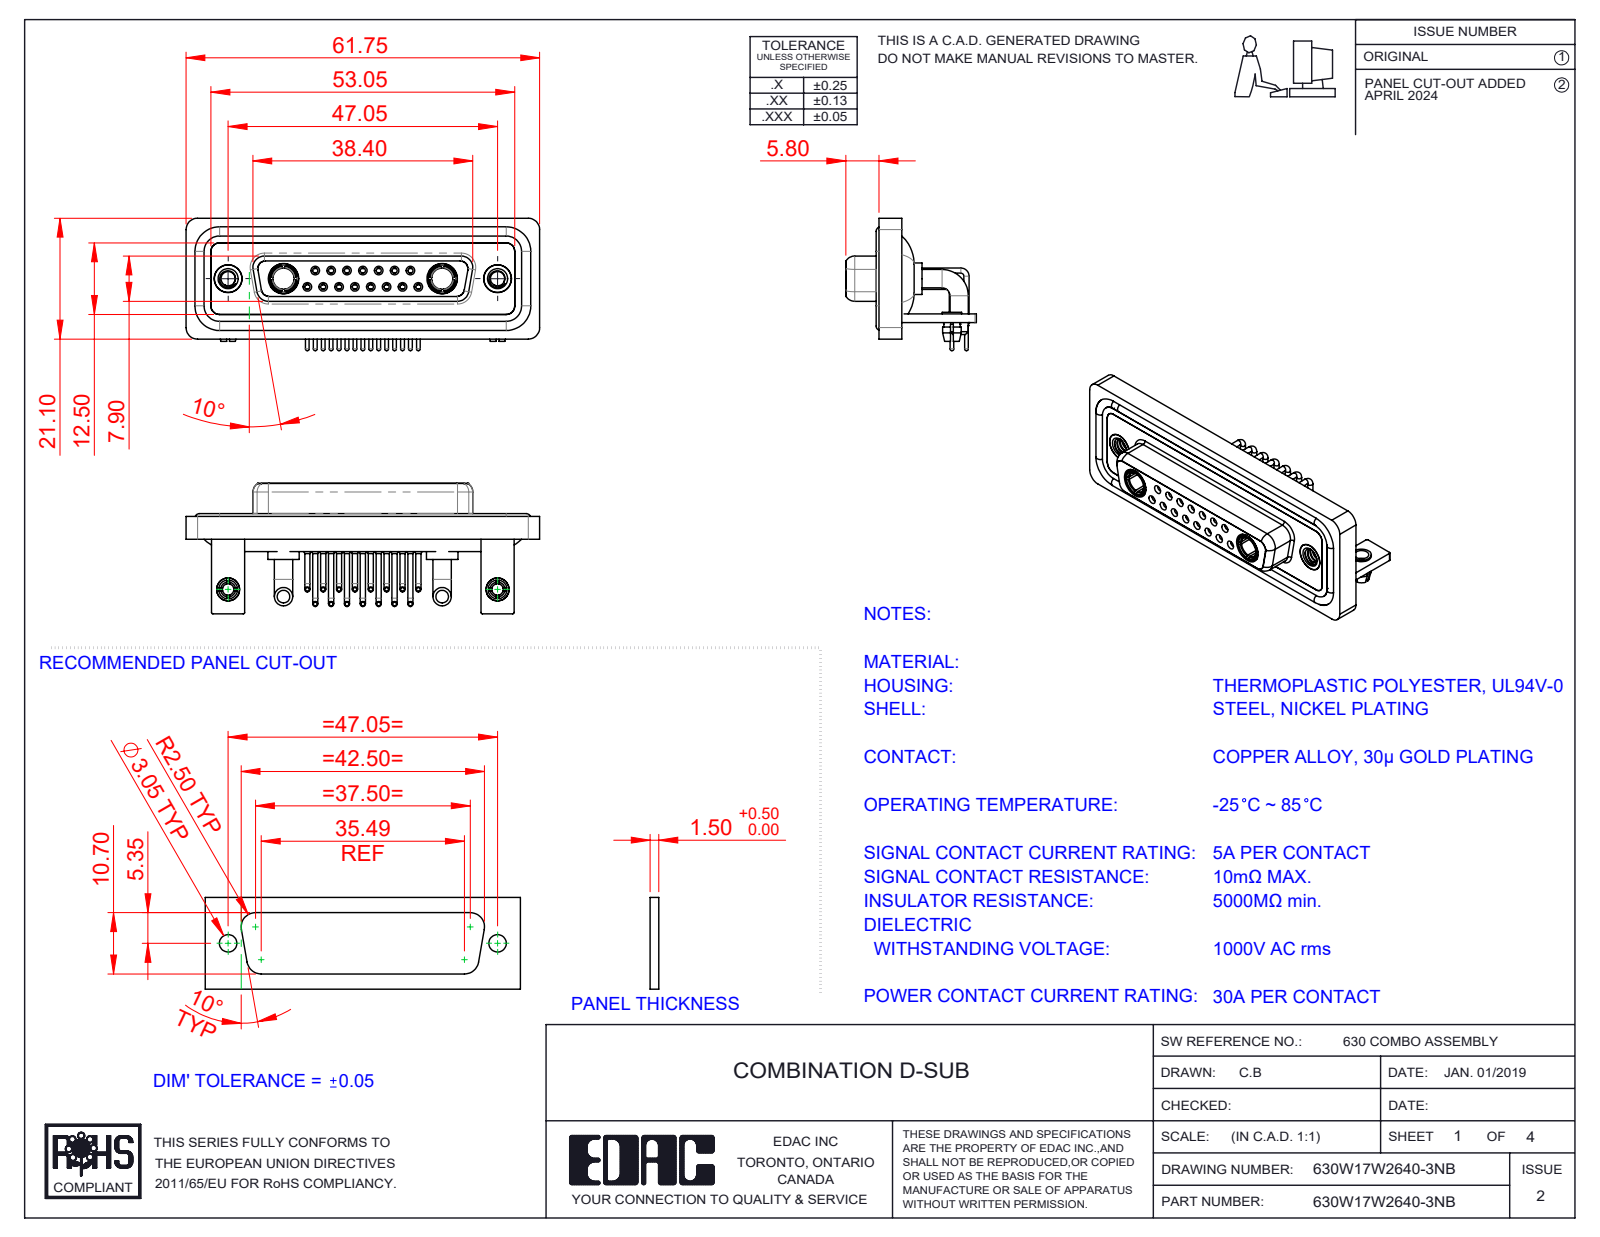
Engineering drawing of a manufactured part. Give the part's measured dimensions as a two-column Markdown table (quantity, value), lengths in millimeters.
| quantity | value |
| --- | --- |
| part name | 630Combo Threaded Rivet_A; 630Combo Contact Row 1_50 Contacts; 630Combo Stabilizer Bracket_50 Contacts; 630W17W2640-3NB (+7 more) |
| STEP written by | SolidWorks 2023 (CONFIG_CONTROL_DESIGN) |
| units | millimeters |
| bodies | 30 solids, 1471 faces (456 planar, 637 cylindrical, 378 other) |
| overall size | 61.75 × 23.12 × 22.8 |
| volume | 8 938 mm³ |
| surface area | 15 516 mm² |
| round holes (diameter × count) | 2 × 17, 0.9 × 15, 1.1 × 15, 1.5 × 15, 1.6 × 8, 1.7 × 7, 2.5 × 4, 4.85 × 4, 3.2 × 2, 3.7 × 2, 4 × 2, 4.05 × 2 |
| round bosses / shafts (diameter × count) | 0.9 × 15, 0.65 × 15, 1.6 × 11, 3.2 × 4, 5.5 × 2, 5.2 × 2, 4.96 × 2, 4.95 × 2 |
| partial cylindrical surfaces (radius × count) | 2 × 19, 1.5 × 18, 0.25 × 16, 1.35 × 8, 1.6 × 8, 0.5 × 5, 0.6 × 4, 0.65 × 4 |
| main face-to-face distances | 0.4, 1.8, 2.9, 3.7, 1.5, 4.1, 1.1, 1.4, 1.6, 3.1 |
| hole center spacings | 3.16, 2.77, 5.54, 8.31, 5.04, 7.49, 11.08, 5.03 |
